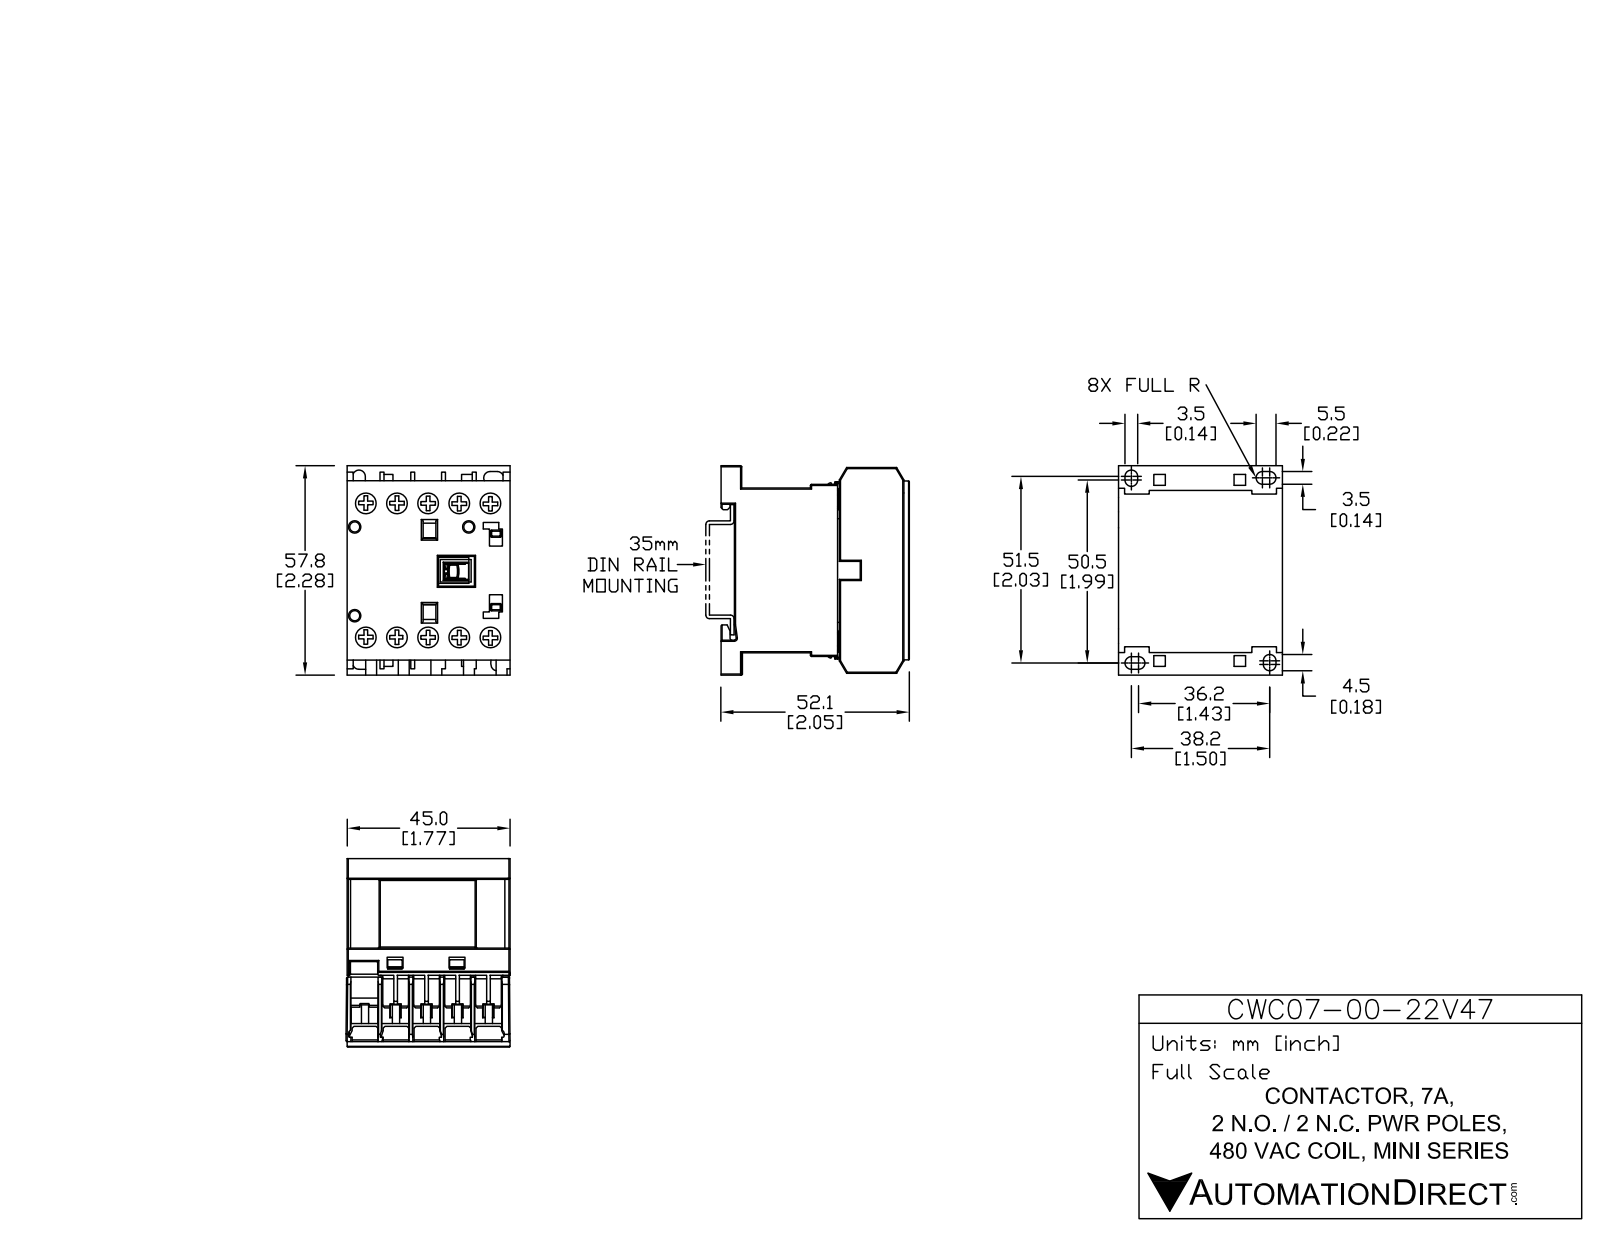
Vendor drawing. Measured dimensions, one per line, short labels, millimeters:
name: CWC07-00-22V47
written by: SolidWorks 2013 (AUTOMOTIVE_DESIGN)
unit: mm
bodies: 15 solids, 535 faces (445 planar, 90 cylindrical, 0 other)
size: 58.04 × 52.12 × 45.75
volume: 97 133 mm³; area: 30 437 mm²
holes: 10× ⌀6.2, 3× ⌀2.8
bosses: 10× ⌀5.9
rounds: 20× R0.3, 6× R1.72, 2× R1.73, 1× R0.32, 1× R0.42, 1× R0.55
face distances: 8.25, 45.5, 1.25, 16.5, 9.5, 5.5, 17.75, 5.13, 10.63, 7
hole spacings: 8.55, 37.94, 17.1, 40.72, 36.96, 25.65, 44.99, 6.91
